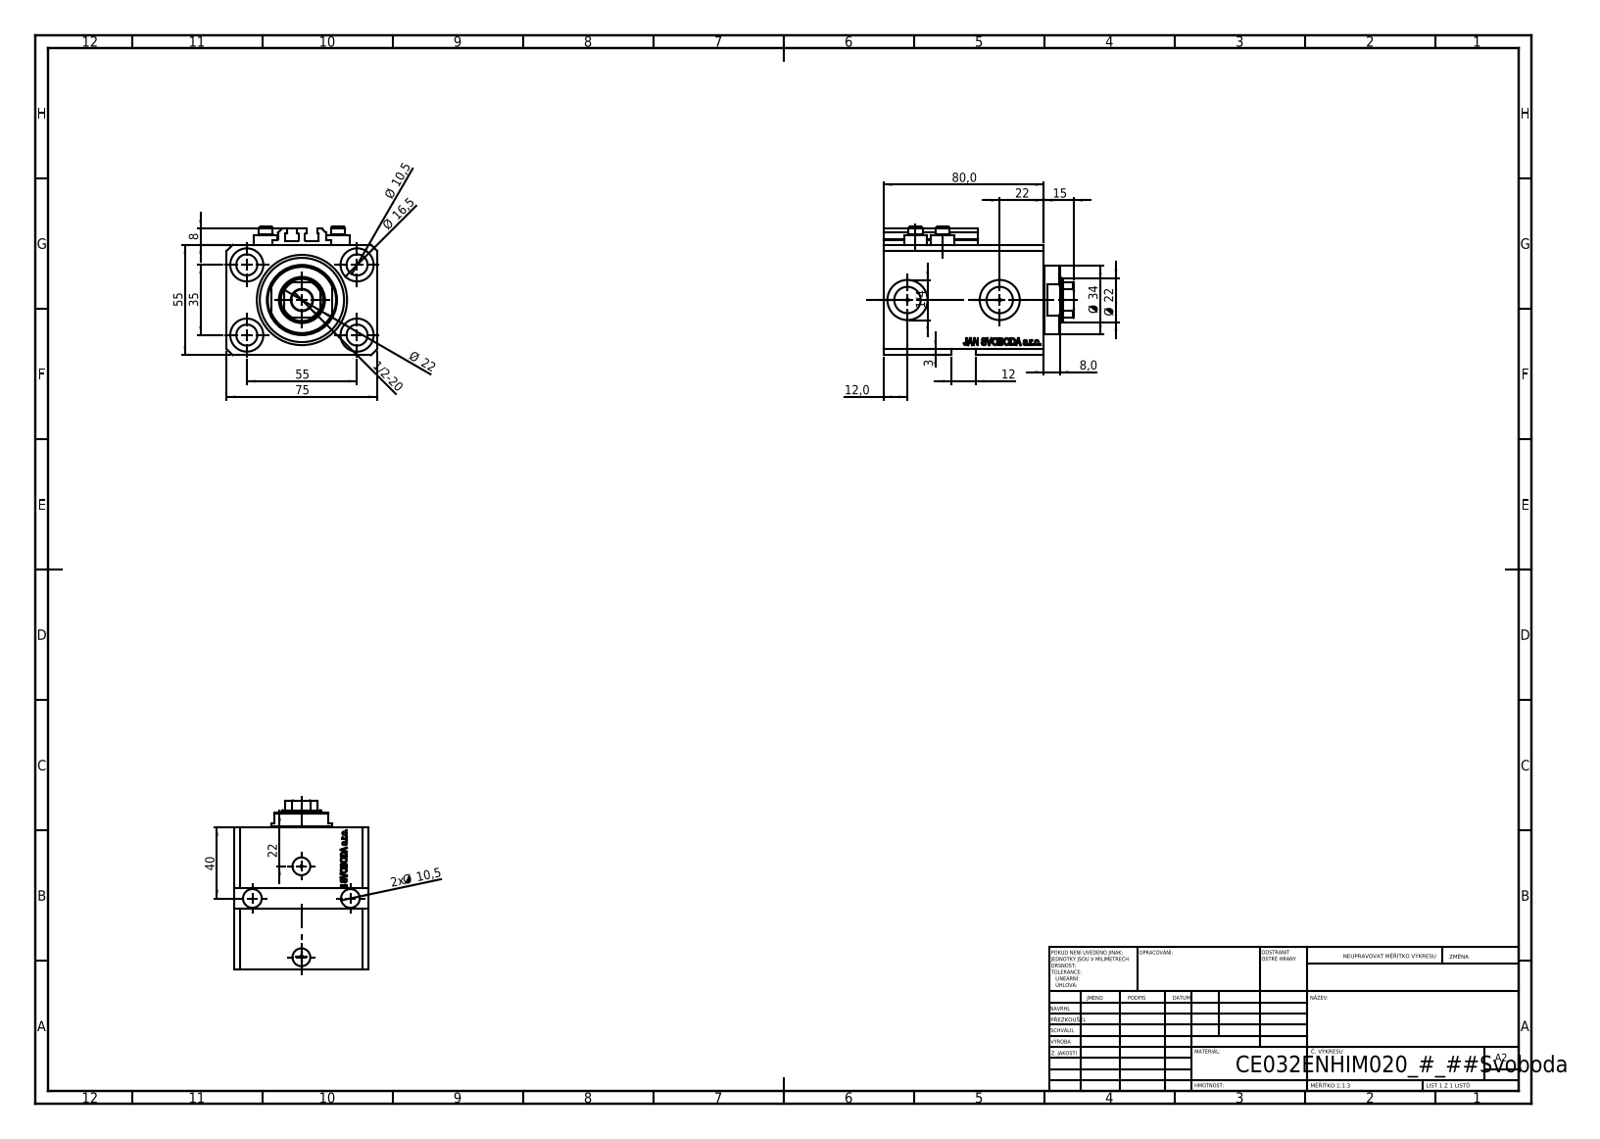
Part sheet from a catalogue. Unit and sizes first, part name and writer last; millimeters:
Units: millimetres
Overall size (bounding box): 95 × 75 × 64
Round holes (diameter × count): ⌀10.5 ×7, ⌀1.25 ×4, ⌀4 ×4, ⌀16.5 ×4, ⌀10 ×2, ⌀13.16 ×2, ⌀20 ×2, ⌀22 ×1, ⌀32 ×1, ⌀45 ×1
Round bosses / shafts (diameter × count): ⌀11.6 ×4, ⌀7 ×4, ⌀34 ×1
Partial cylindrical surfaces — rounded edges, fillets, slot ends (radius × count): R0.2 ×10, R10.5 ×1
Main face-to-face distances: 55, 75, 15, 80, 65, 3, 55.1, 9.9, 70.1, 54
Hole centre spacings: 32.6, 55, 13.6, 14.09, 19.89, 20.12, 25.81, 28.48
Volume: 283 894 mm³ · Surface area: 74 463 mm²
Bodies: 8 solids, 1064 faces (514 planar, 126 cylindrical, 424 other)
Part name (STEP PRODUCT): V250CE_E_Body; V250CE_C_VCP; V250CE_VC_E; ALLEN BOLT V250CE
STEP written by: SolidWorks 2019 (CONFIG_CONTROL_DESIGN)
